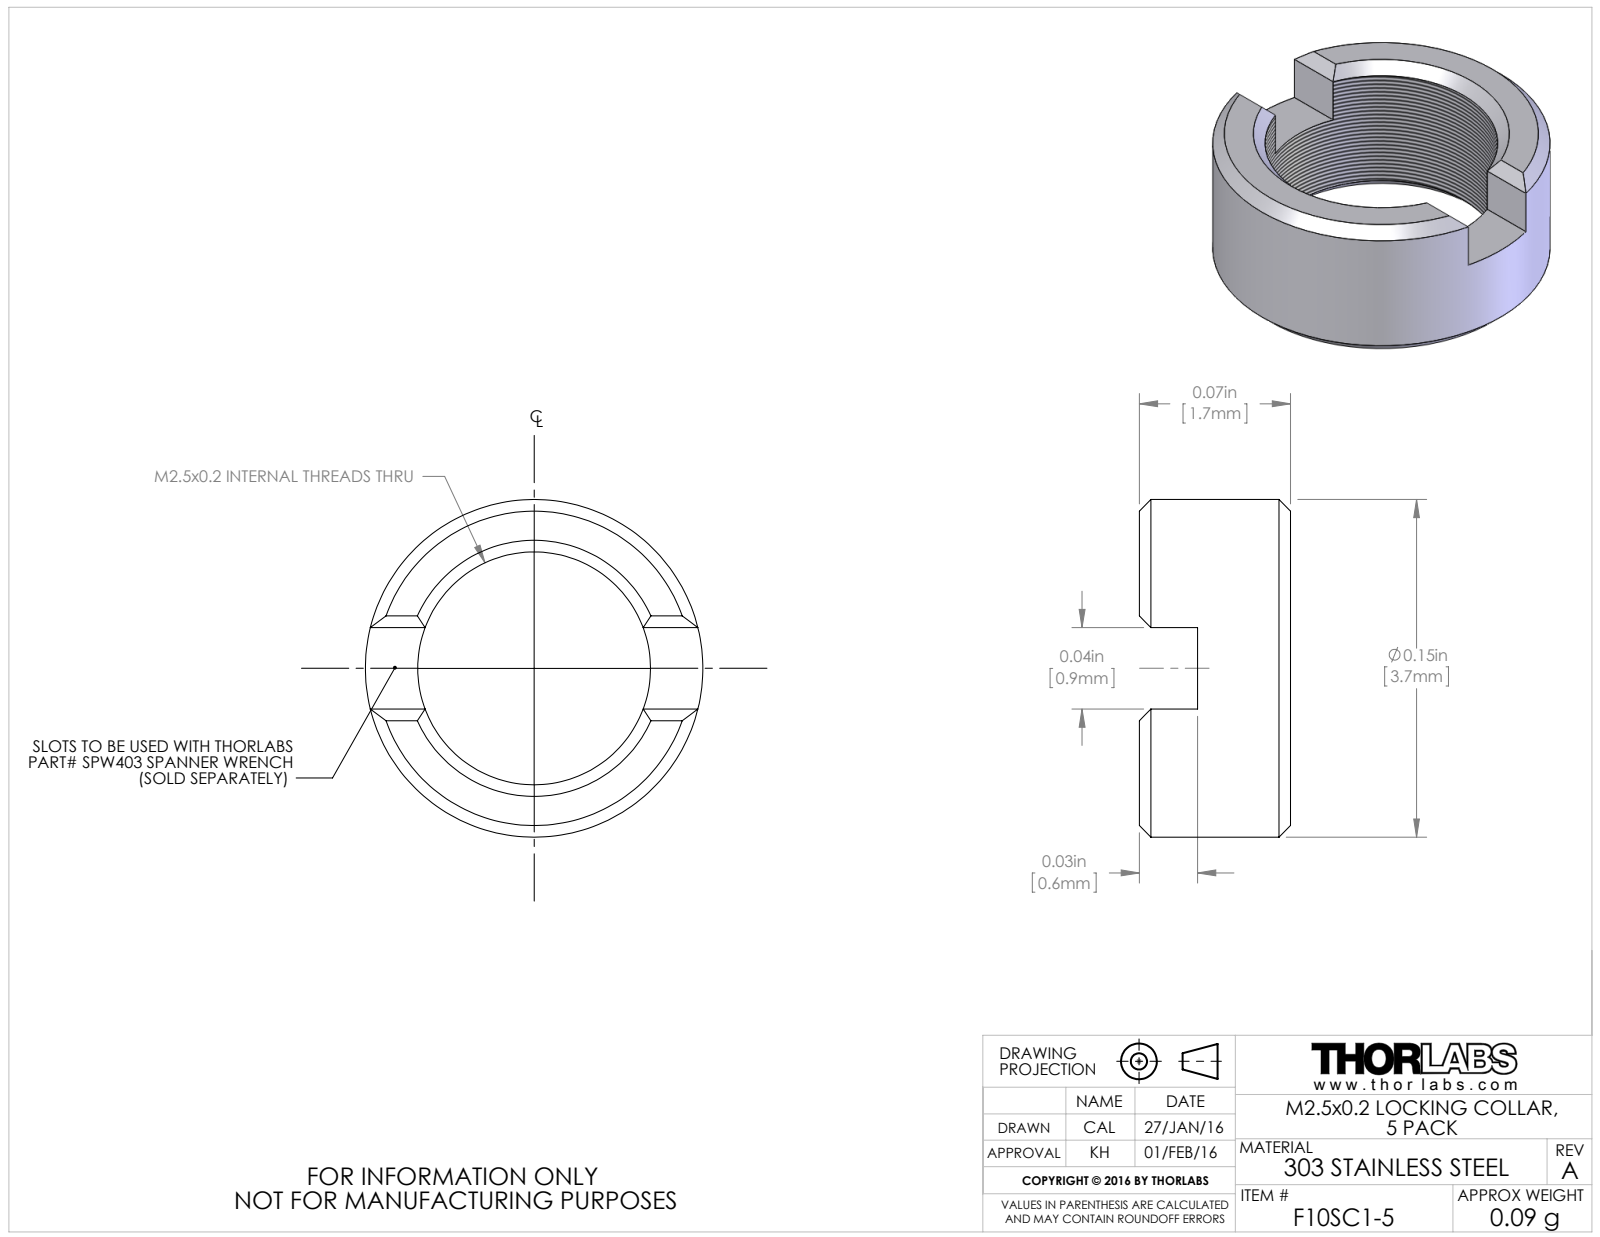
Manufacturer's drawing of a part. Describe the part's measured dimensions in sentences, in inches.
The part is named "TTN090964-E0W". Its 3-D file was written by "SolidWorks 2014 (AUTOMOTIVE_DESIGN)". It is 1 solid with 27 faces: 13 planar, 4 cylindrical and 10 other. Overall it measures 0.145 by 0.145 by 0.065 inches. Its volume is 0.001 cubic inches and its surface area 0.062 square inches. Round holes: 1 of diameter 0.1. Round bosses or shafts: 1 of diameter 0.145. The main face-to-face distances are 0.065, 0.04, 0.025, 0.035.
